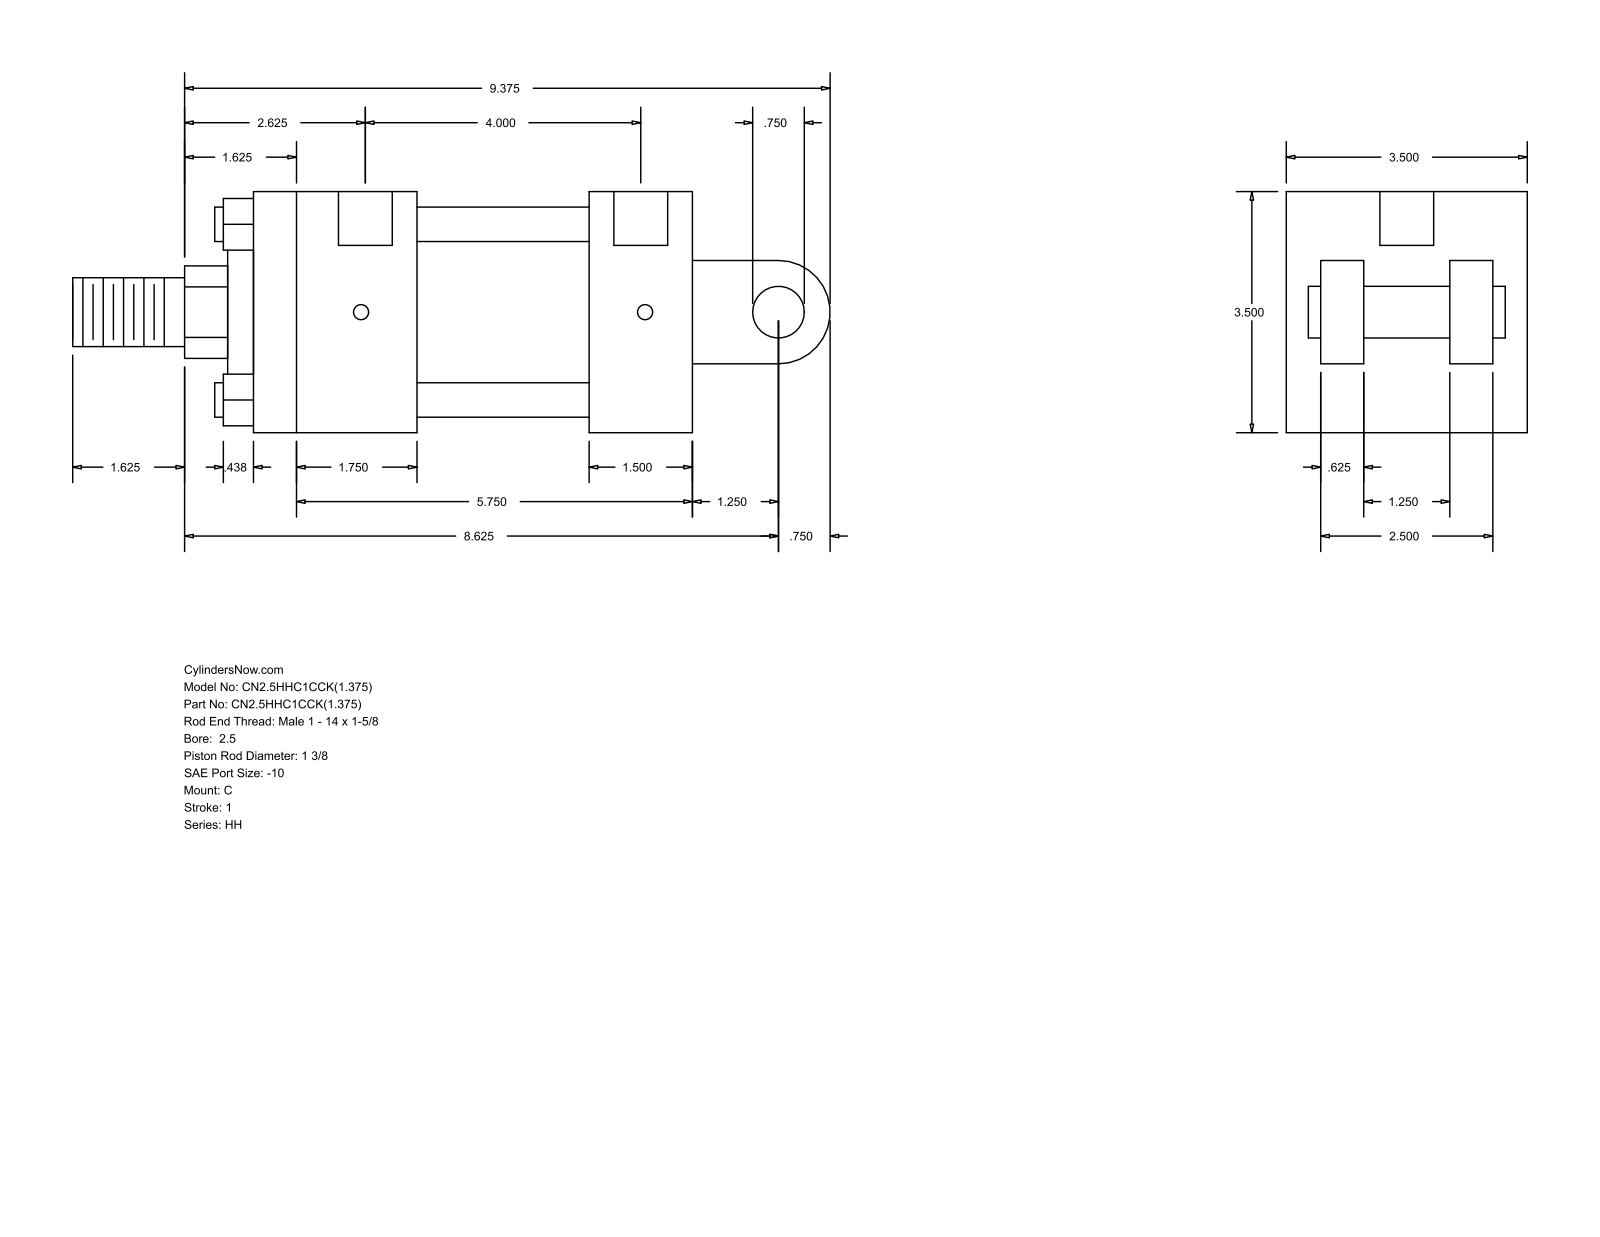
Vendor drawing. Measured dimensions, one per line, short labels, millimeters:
name: HH_C__0250_1.375
written by: GSSL Pune (CONFIG_CONTROL_DESIGN)
unit: mm
bodies: 0 solids, 99 faces (70 planar, 29 cylindrical, 0 other)
size: 279.4 × 88.9 × 88.9
holes: 4× ⌀5.56, 2× ⌀19.84
bosses: 4× ⌀12.7, 1× ⌀73.03, 1× ⌀50.8, 1× ⌀34.92, 1× ⌀25.4, 1× ⌀19.05
rounds: 1× R17.06, 1× R19.05
face distances: 88.9, 63.5, 161.92, 38.1, 12.7, 123.82, 60.32, 101.6, 76.2, 28.57
hole spacings: 1.58, 103.19, 104.77, 101.61
